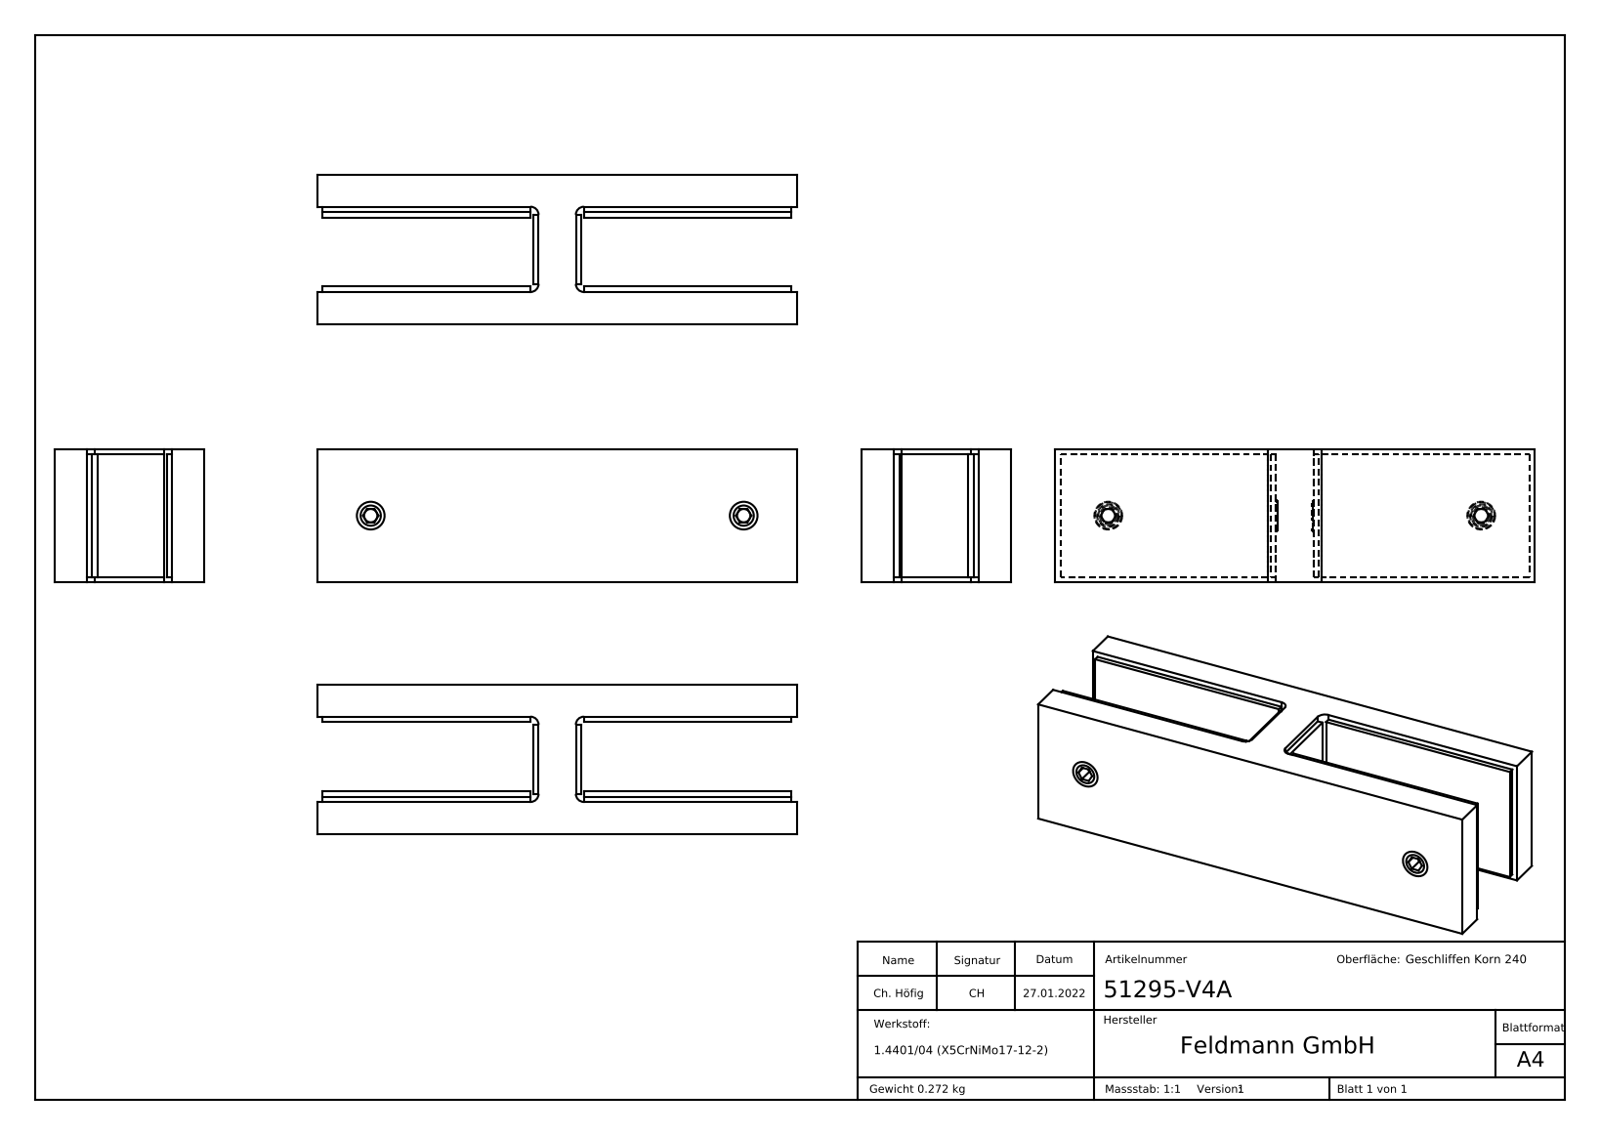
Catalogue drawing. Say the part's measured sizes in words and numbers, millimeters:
The part is named "51295-V4A Teil2; DIN913_DIN 913 M5x6; DIN913; 51295-V4A Teil4_51295-V4A Teil4 (+7 more)". Its 3-D file was written by "SolidWorks 2018 (CONFIG_CONTROL_DESIGN)". It is 11 solids with 434 faces: 278 planar, 20 cylindrical and 136 other. Overall it measures 70000 by 5000 by 5000 millimeters. Its volume is 35 815 cubic millimeters and its surface area 25 630 square millimeters. Round holes: 2 of diameter 4.2. Round bosses or shafts: 2 of diameter 5. Partial cylindrical surfaces (rounded edges, fillets, slot ends): 4 of radius 0.5, 4 of radius 1.5. The main face-to-face distances are 1, 15, 7, 6, 22, 21, 16, 14, 8, 28. The hole center spacings are 70.
